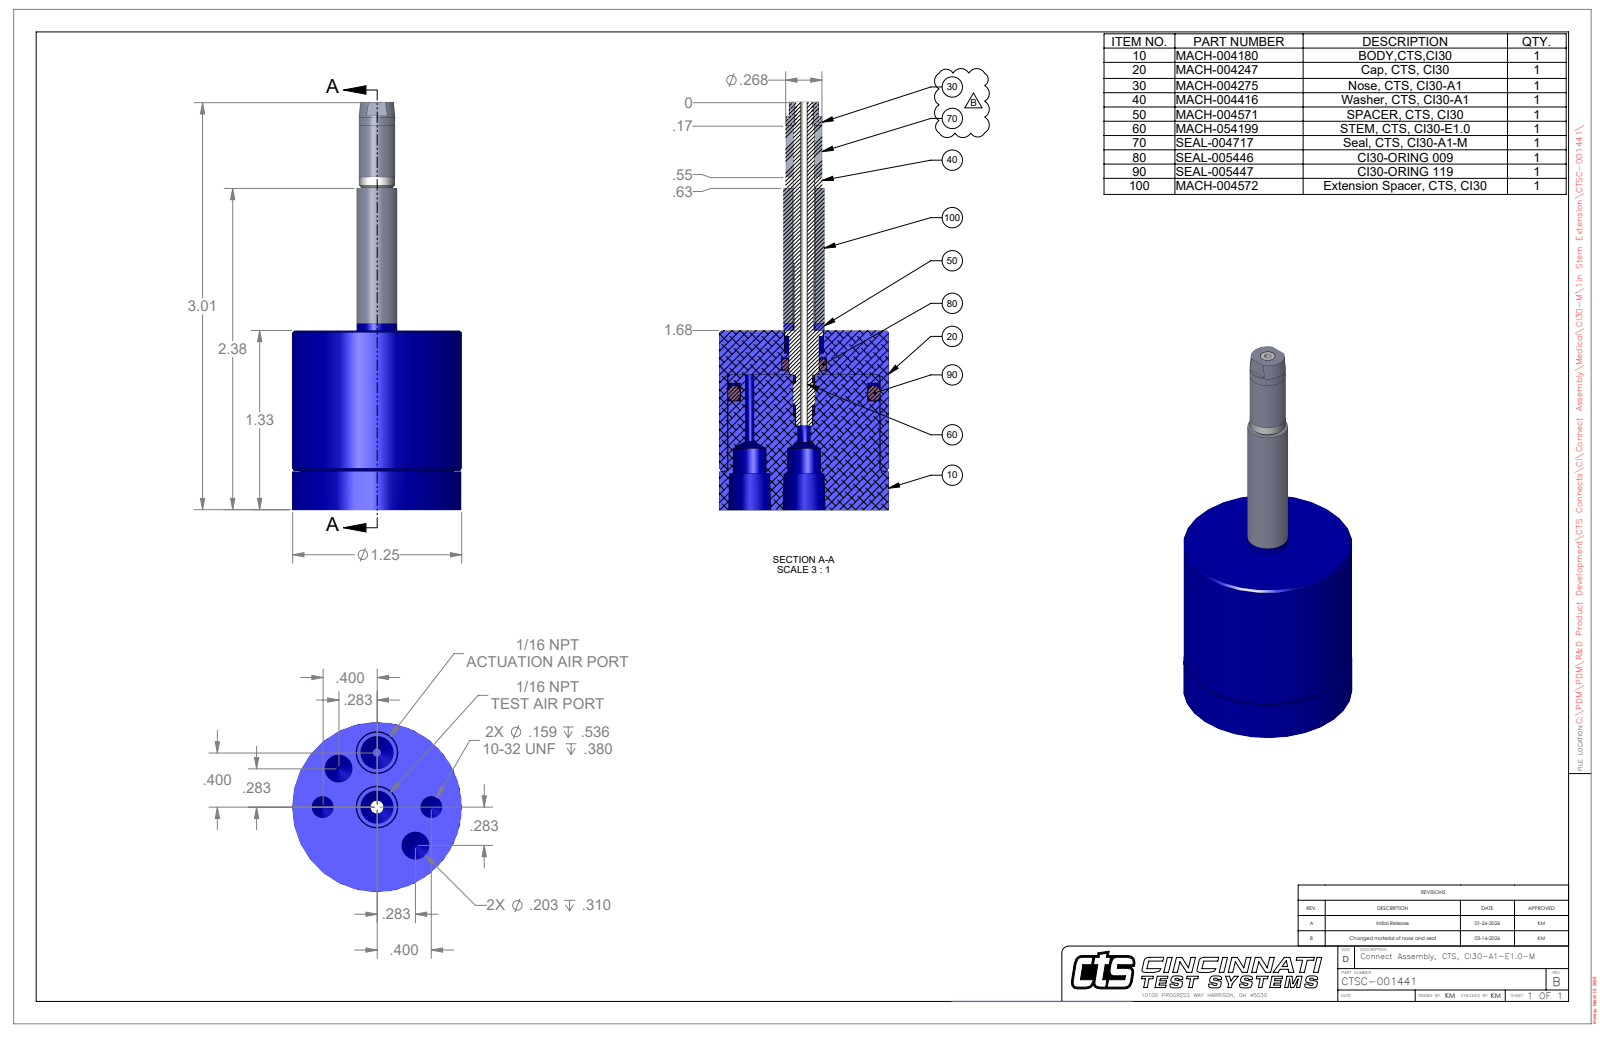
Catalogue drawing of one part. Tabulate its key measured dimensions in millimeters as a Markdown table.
| quantity | value |
| --- | --- |
| part name | CTSC-001441 |
| STEP written by | SolidWorks 2023 (AUTOMOTIVE_DESIGN) |
| units | millimeters |
| bodies | 6 solids, 71 faces (34 planar, 25 cylindrical, 12 other) |
| overall size | 76.43 × 31.75 × 31.75 |
| volume | 26 998 mm³ |
| surface area | 8 432 mm² |
| round holes (diameter × count) | 4.04 × 2, 5.16 × 2, 6.15 × 2, 1.32 × 1, 2.38 × 1, 2.87 × 1, 3.94 × 1, 4.18 × 1, 7.34 × 1 |
| round bosses / shafts (diameter × count) | 31.75 × 1, 30.64 × 1, 7.62 × 1, 7.04 × 1, 6.81 × 1, 3.94 × 1, 3.51 × 1 |
| main face-to-face distances | 33.66, 7, 26.66, 34.93, 27.93, 1.27, 72.01, 65.01, 38.35, 37.08 |
| hole center spacings | 7.77, 10.16, 18.77, 10.15, 14.37, 20.31, 20.32 |
